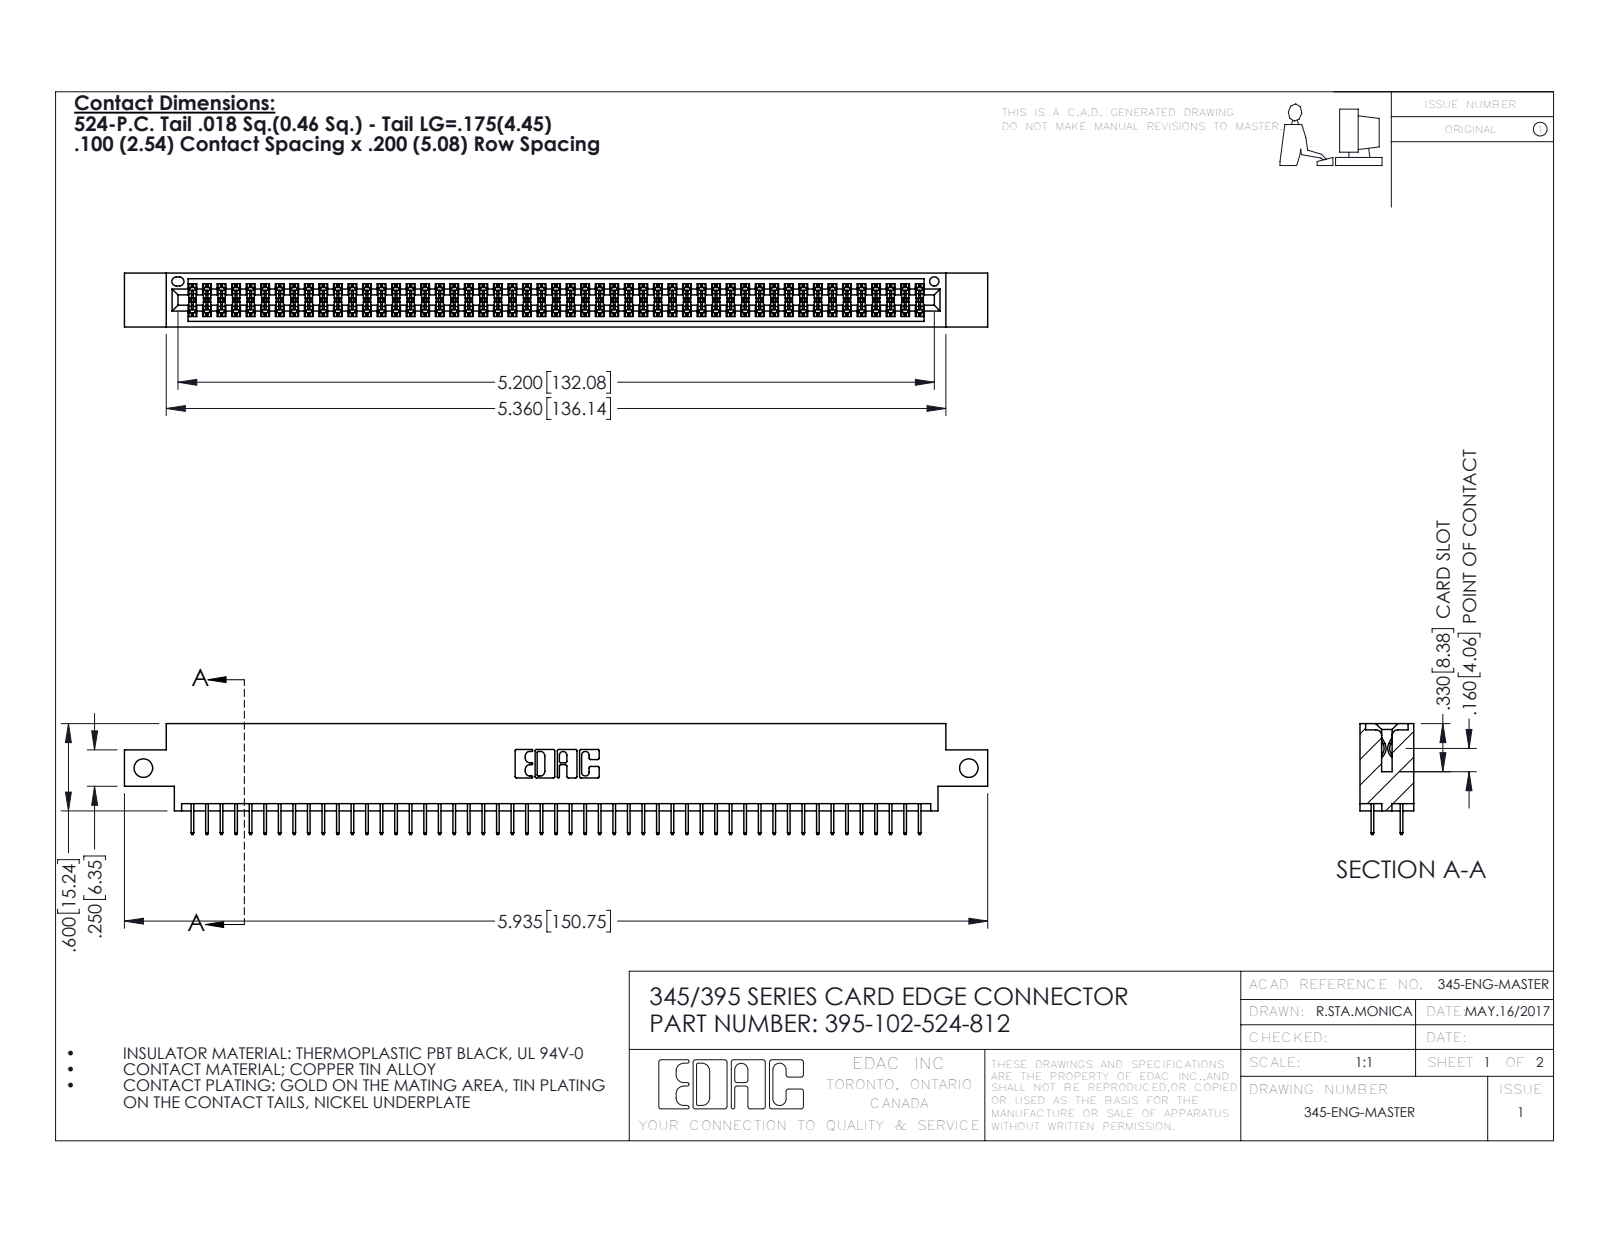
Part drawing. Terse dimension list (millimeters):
name: 345-292-001_345-293-124; 395-102-524-812; 345 Part_0.170 Offset - Side Mount
written by: SolidWorks 2016 (CONFIG_CONTROL_DESIGN)
unit: mm
bodies: 103 solids, 5638 faces (4062 planar, 1576 cylindrical, 0 other)
size: 150.7 × 19.4 × 9.4
volume: 14 400 mm³; area: 21 020 mm²
holes: 2× ⌀3.3, 1× ⌀1.6
rounds: 153× R0.2, 22× R0.3, 6× R0.2, 6× R0.8, 3× R0.7, 2× R0.4, 2× R0.5, 2× R0.6
face distances: 1.8, 7.6, 9.4, 5.1, 2.5, 6.9, 0.6, 5.7, 4.4, 1.8
hole spacings: 144.1
